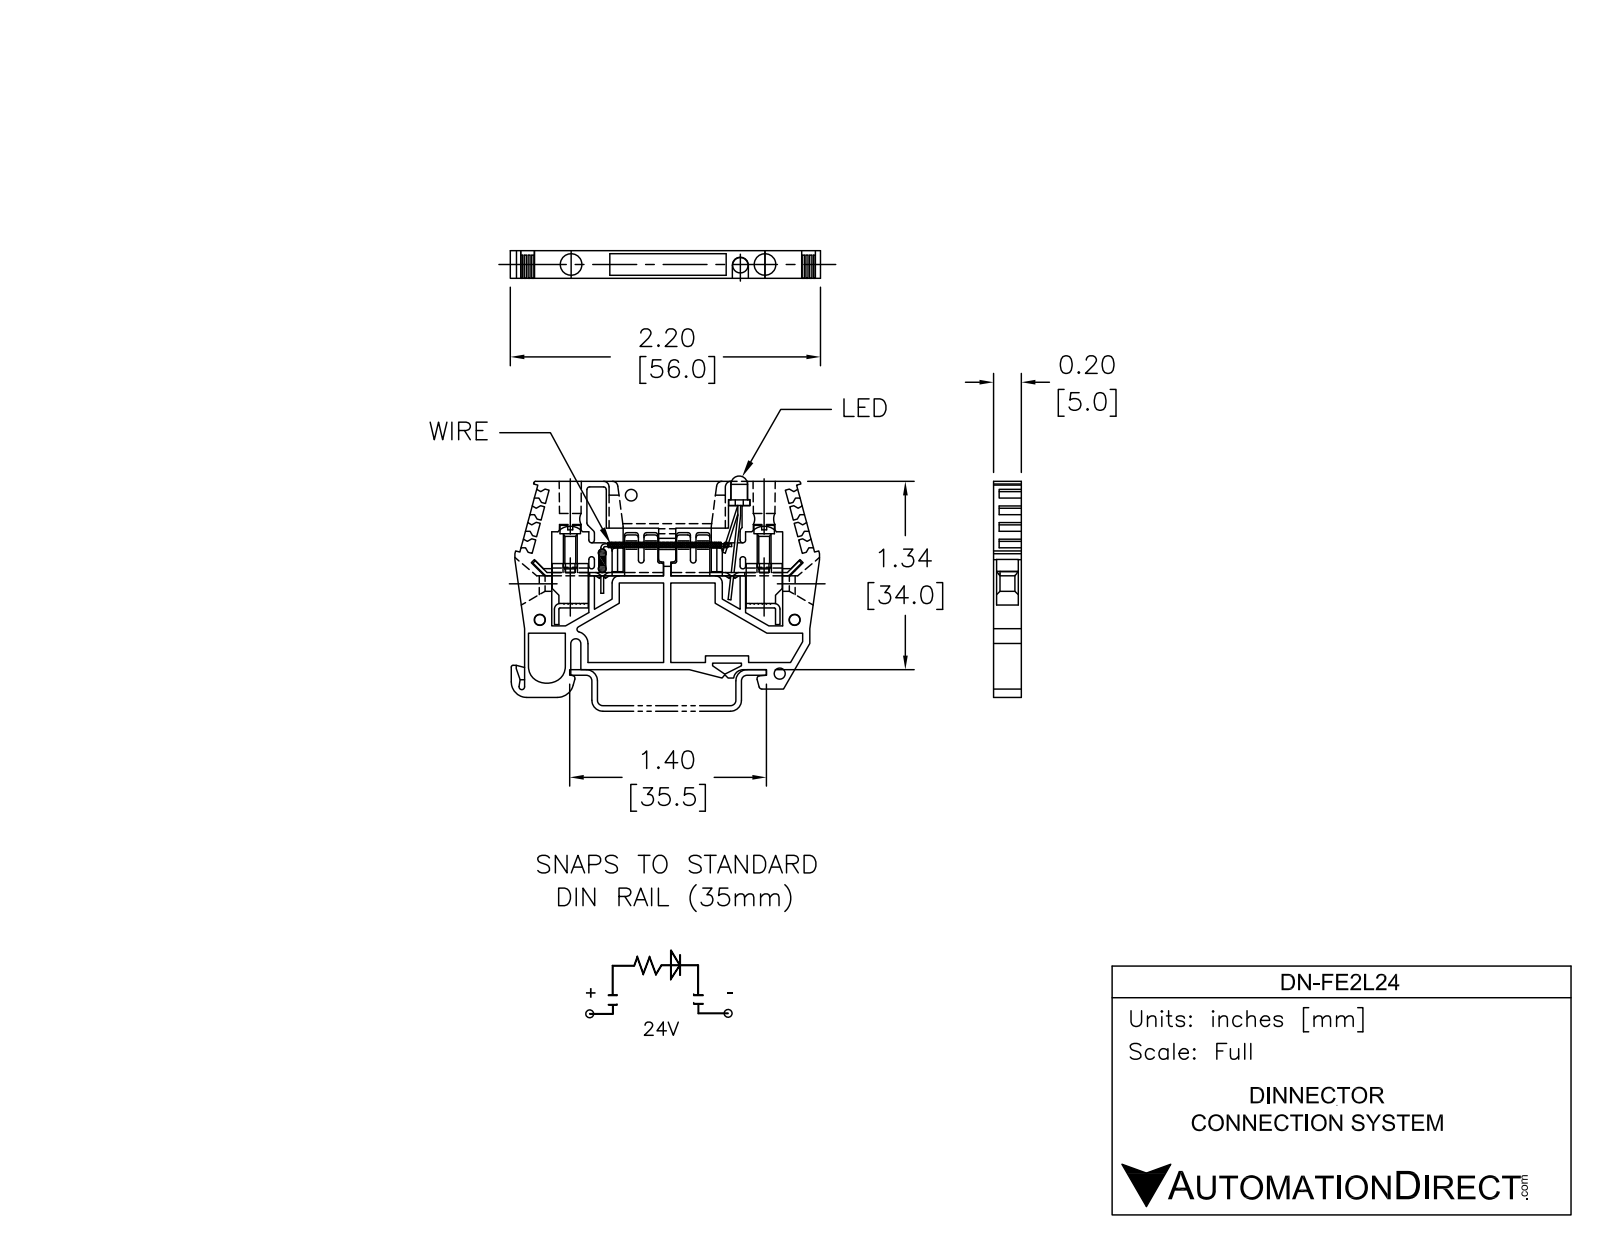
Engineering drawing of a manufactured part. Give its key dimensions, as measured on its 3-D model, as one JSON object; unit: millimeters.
{"part_name": "4258000_DN-QFE2_1; 4358001_DN-FE2L24; 20621_1", "step_written_by": "SolidWorks 2013 (AUTOMOTIVE_DESIGN)", "units": "millimeters", "bodies": {"solids": 2, "faces": 338, "planar": 199, "cylindrical": 86, "other": 53}, "overall_size": [55.65, 39.6, 5], "volume_mm3": 7520, "surface_area_mm2": 6016, "round_holes": [[2, 3], [4.1, 2]], "round_bosses_or_shafts": [[0.3, 10], [4, 1], [3, 1]], "partial_cylinders_radius": [[0.5, 11], [3, 5], [1, 3], [0.9, 1], [1.05, 1], [1.7, 1], [1.95, 1], [2.8, 1]], "face_to_face_distances": [5, 34, 2.2, 0.55, 4.45, 1, 3.1, 3.45, 3.6, 1.4], "hole_center_spacings": [10.07, 35, 44.38, 46]}
